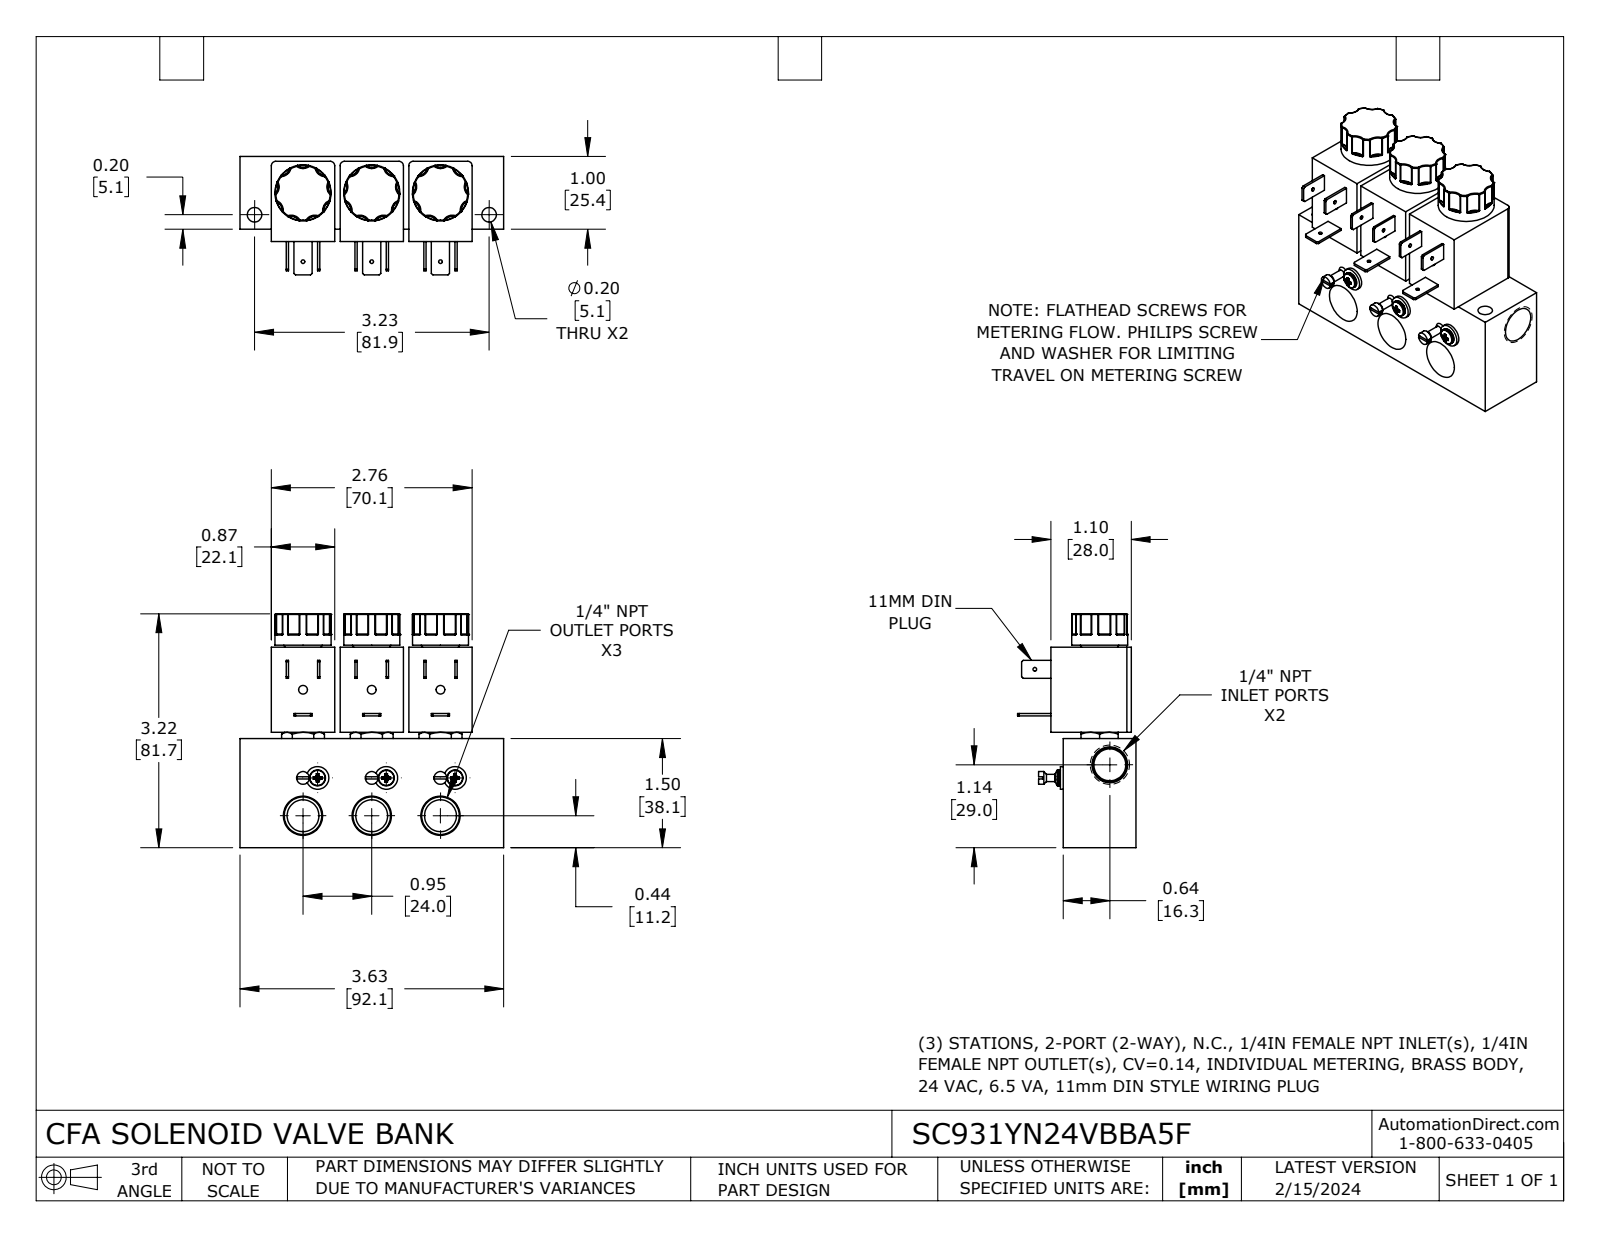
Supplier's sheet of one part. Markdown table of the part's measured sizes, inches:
| quantity | value |
| --- | --- |
| part name | SC931YN24VBBA5F |
| STEP written by | SolidWorks 2023 (CONFIG_CONTROL_DESIGN) |
| units | inches |
| bodies | 1 solid, 829 faces (215 planar, 197 cylindrical, 417 other) |
| overall size | 3.625 × 3.215 × 1.627 |
| volume | 8.838 in³ |
| surface area | 53.67 in² |
| round holes (diameter × count) | 0.05 × 4, 0.438 × 4, 0.12 × 3, 0.2 × 2 |
| round bosses / shafts (diameter × count) | 0.77 × 3, 0.312 × 3, 0.219 × 3, 0.175 × 3, 0.1 × 3 |
| partial cylindrical surfaces (radius × count) | 0.01 × 54, 0.133 × 27, 0.06 × 6 |
| main face-to-face distances | 1, 0.945, 1.169, 0.169, 1.5, 0.945, 1.89, 0.065, 0.935, 1.104 |
| hole center spacings | 0.945, 0.945, 1.732, 1.89, 1.973, 1.973, 2.564, 0.928 |
